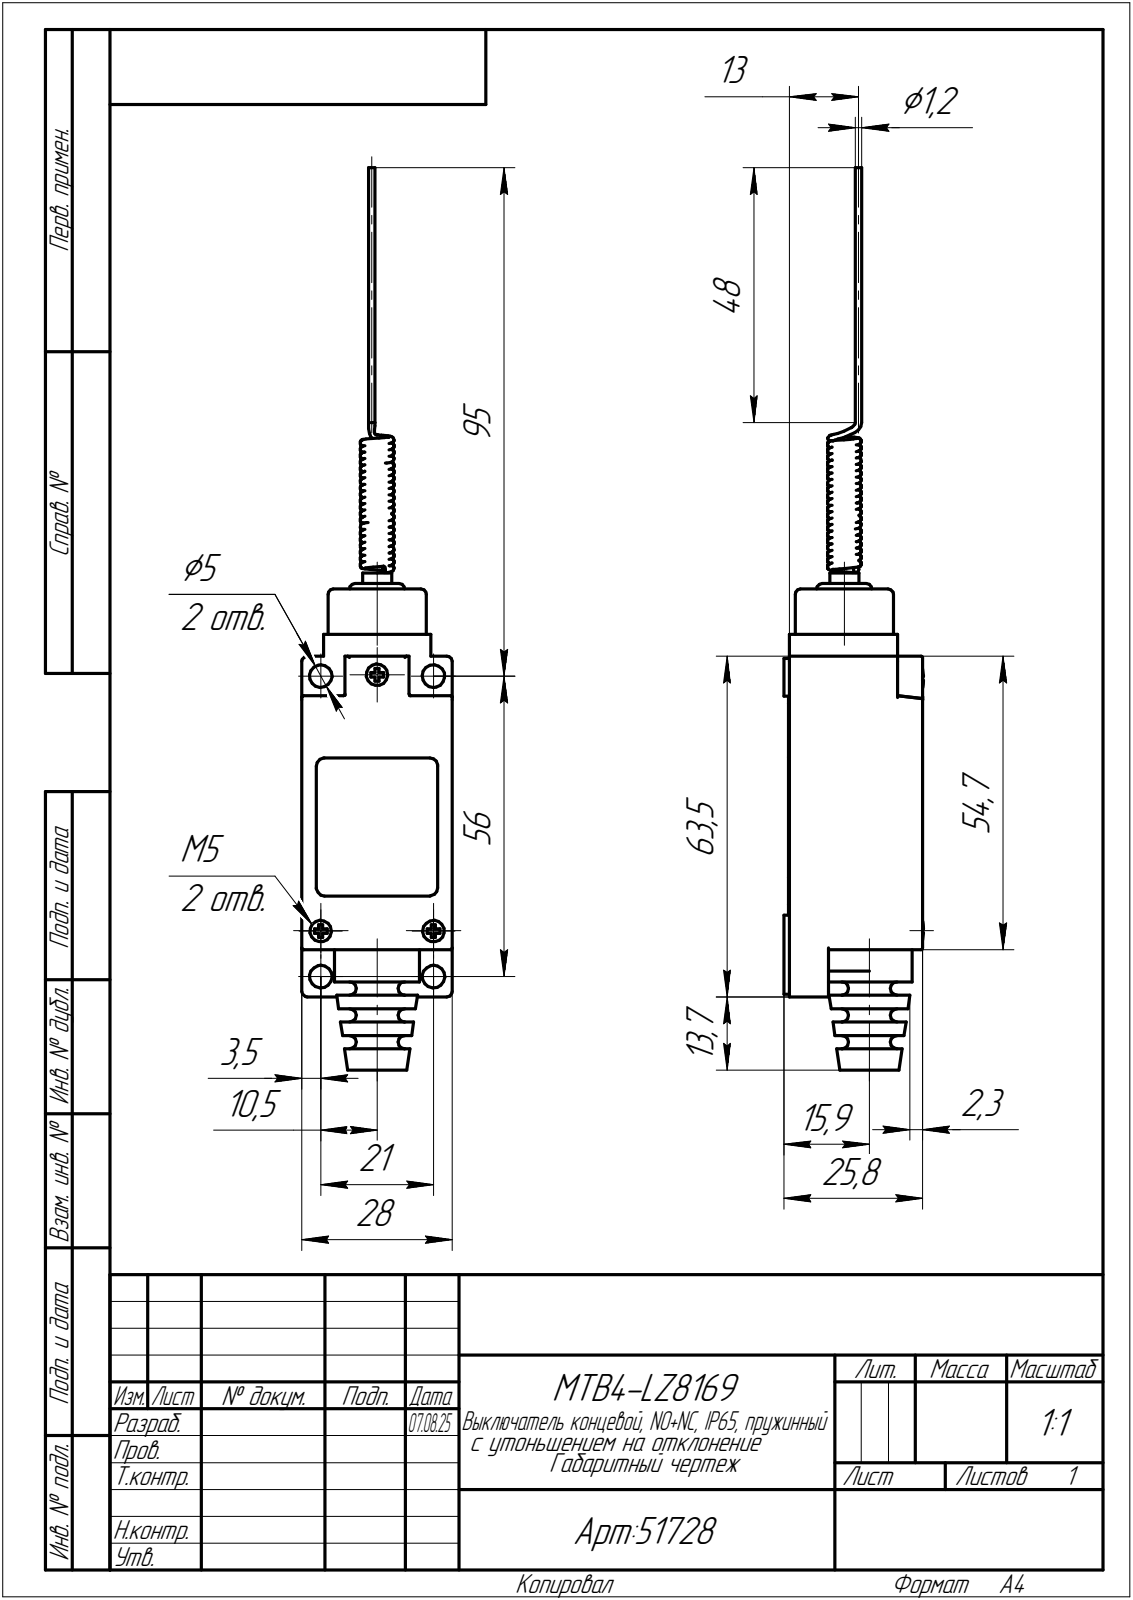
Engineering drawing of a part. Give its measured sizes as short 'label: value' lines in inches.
name: MTB4-LZ8169
written by: C3D Toolkit (CONFIG_CONTROL_DESIGN)
unit: in
bodies: 2 solids, 499 faces (419 planar, 43 cylindrical, 37 other)
size: 6.622 × 1.102 × 1.023
volume: 2.755 in³; area: 19.43 in²
holes: 4× ⌀0.165, 3× ⌀0.244, 1× ⌀0.236
bosses: 3× ⌀0.197, 1× ⌀0.72, 1× ⌀0.622, 1× ⌀0.213, 1× ⌀0.047
rounds: 13× R0.012, 4× R0.039, 4× R0.059, 3× R0.069
face distances: 1.102, 0.976, 0.969, 0.157, 0.295, 0.098, 0.039, 0.185, 0.335, 2.646
hole spacings: 0.827, 0.337, 0.414, 0.893, 1.868, 1.896, 2.043, 2.205
